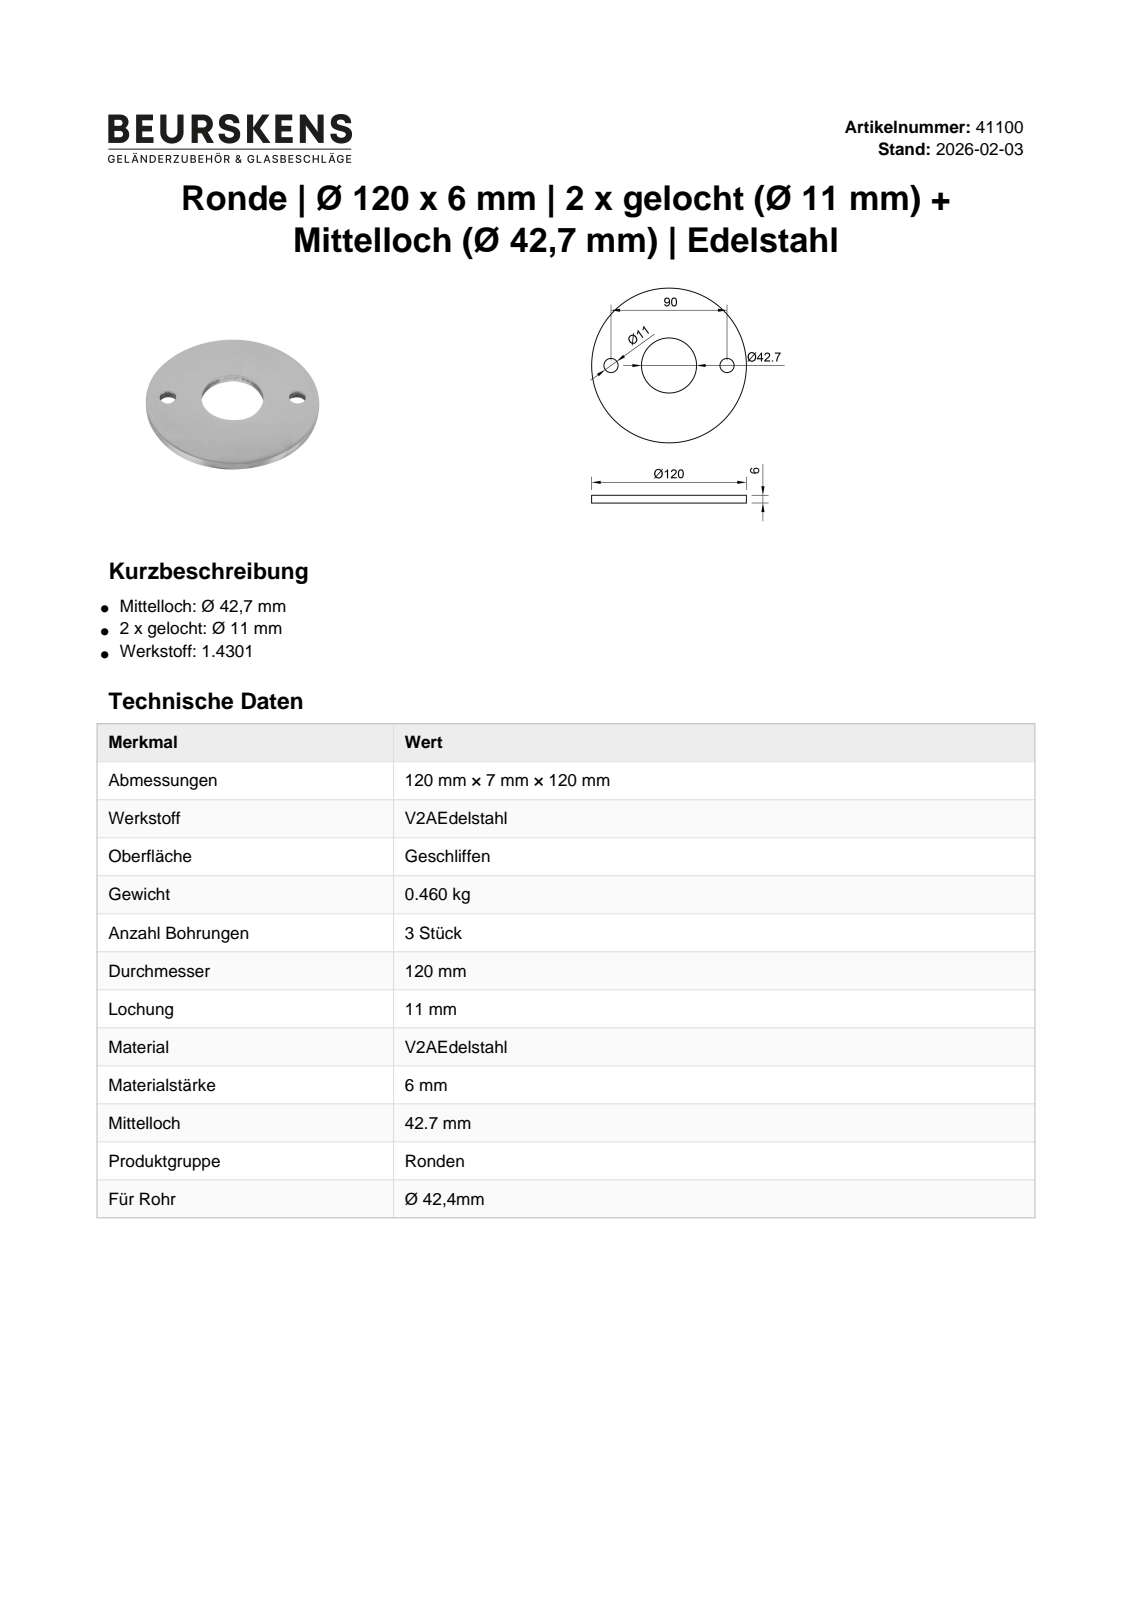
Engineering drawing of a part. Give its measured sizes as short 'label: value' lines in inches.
name: 41100
written by: Autodesk Inventor 2022 (AUTOMOTIVE_DESIGN)
unit: in
bodies: 1 solid, 6 faces (2 planar, 4 cylindrical, 0 other)
size: 4.724 × 4.724 × 0.236
volume: 3.547 in³; area: 35.43 in²
holes: 2× ⌀0.433, 1× ⌀1.681
bosses: 1× ⌀4.724
face distances: 0.236
hole spacings: 1.772, 3.543
